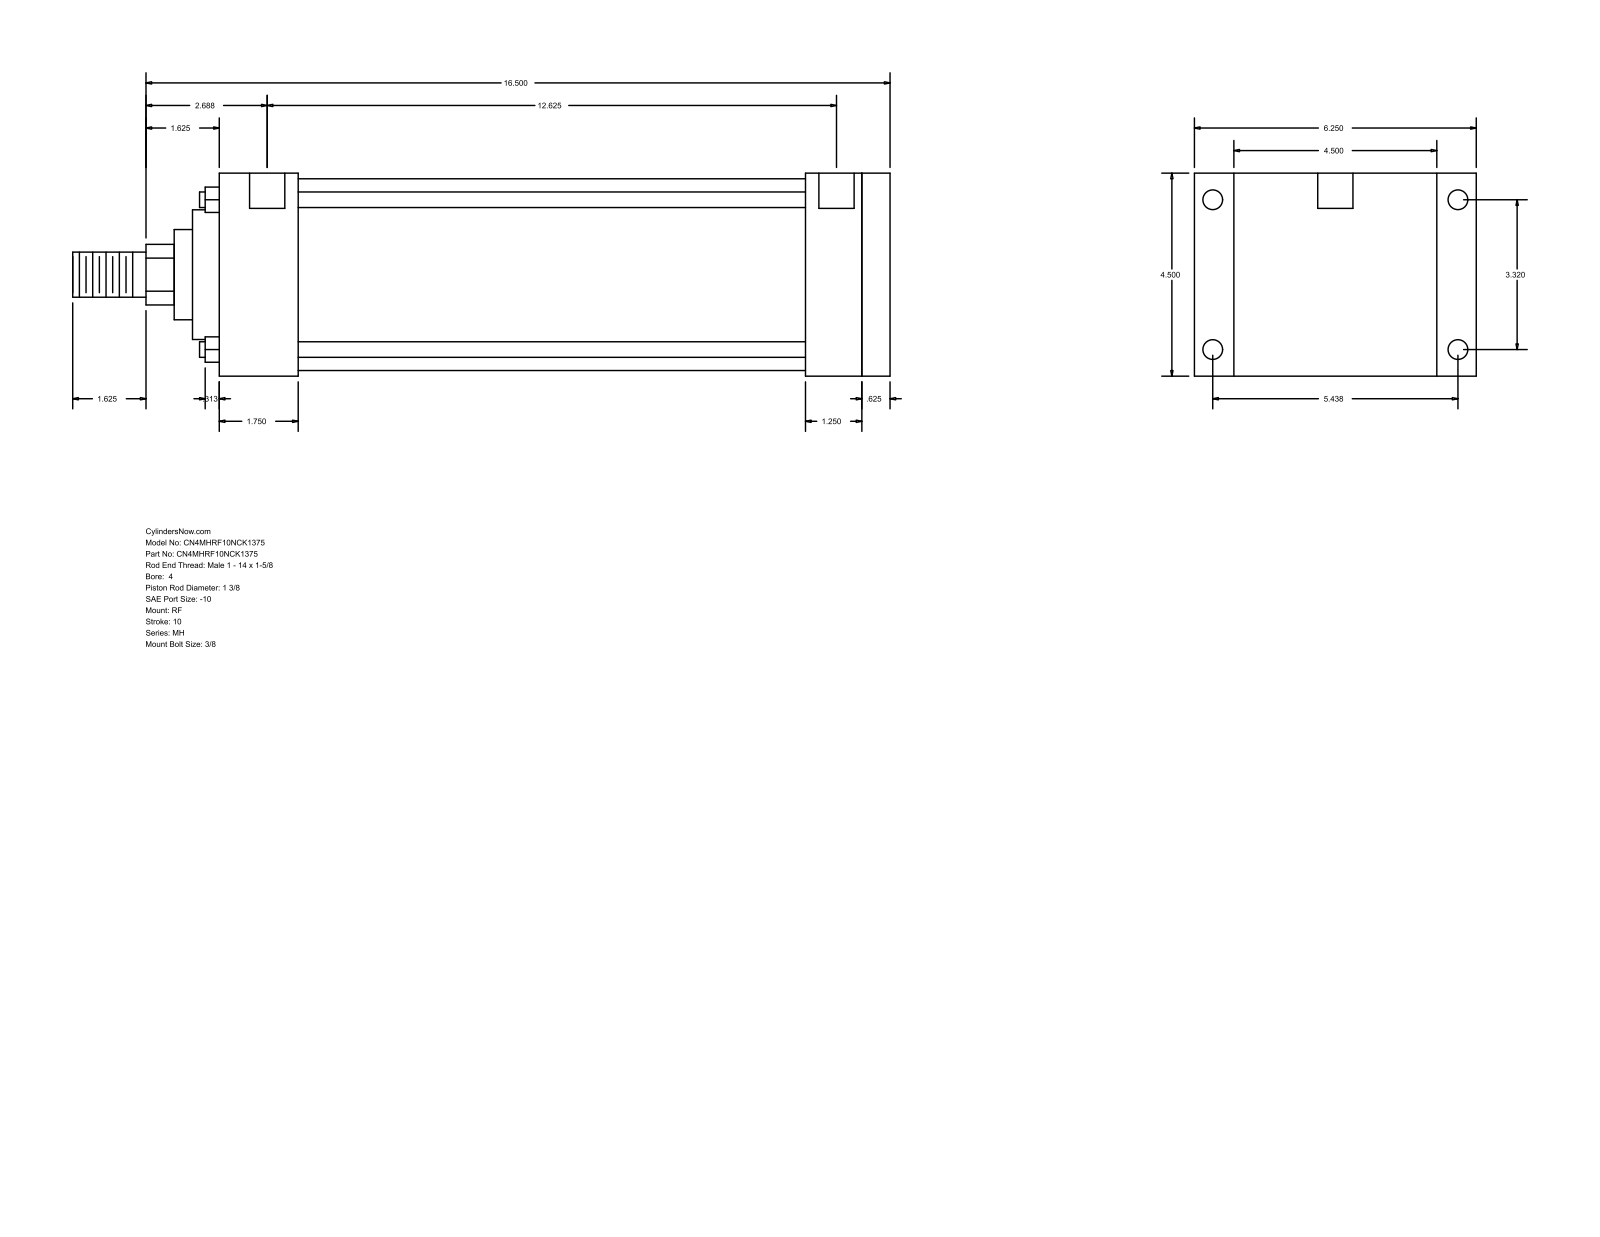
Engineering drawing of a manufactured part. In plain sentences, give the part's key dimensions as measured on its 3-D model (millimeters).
The part is named "MH_RF__0400_1.375". Its 3-D file was written by "GSSL Pune (CONFIG_CONTROL_DESIGN)". It is 0 solids with 94 faces: 65 planar, 29 cylindrical and 0 other. Overall it measures 460.38 by 158.75 by 114.3 millimeters. Round holes: 4 of diameter 8.73, 4 of diameter 11.13, 2 of diameter 19.84. Round bosses or shafts: 4 of diameter 8.76, 1 of diameter 107.95, 1 of diameter 73.03, 1 of diameter 50.8, 1 of diameter 34.92, 1 of diameter 25.4. Partial cylindrical surfaces (rounded edges, fillets, slot ends): 1 of radius 17.06. The main face-to-face distances are 114.3, 377.83, 361.96, 15.87, 44.45, 317.51, 333.38, 330.21, 285.76, 31.75. The hole center spacings are 84.32, 138.12, 161.82, 323.85, 1.58, 1.59, 320.68, 322.26.
